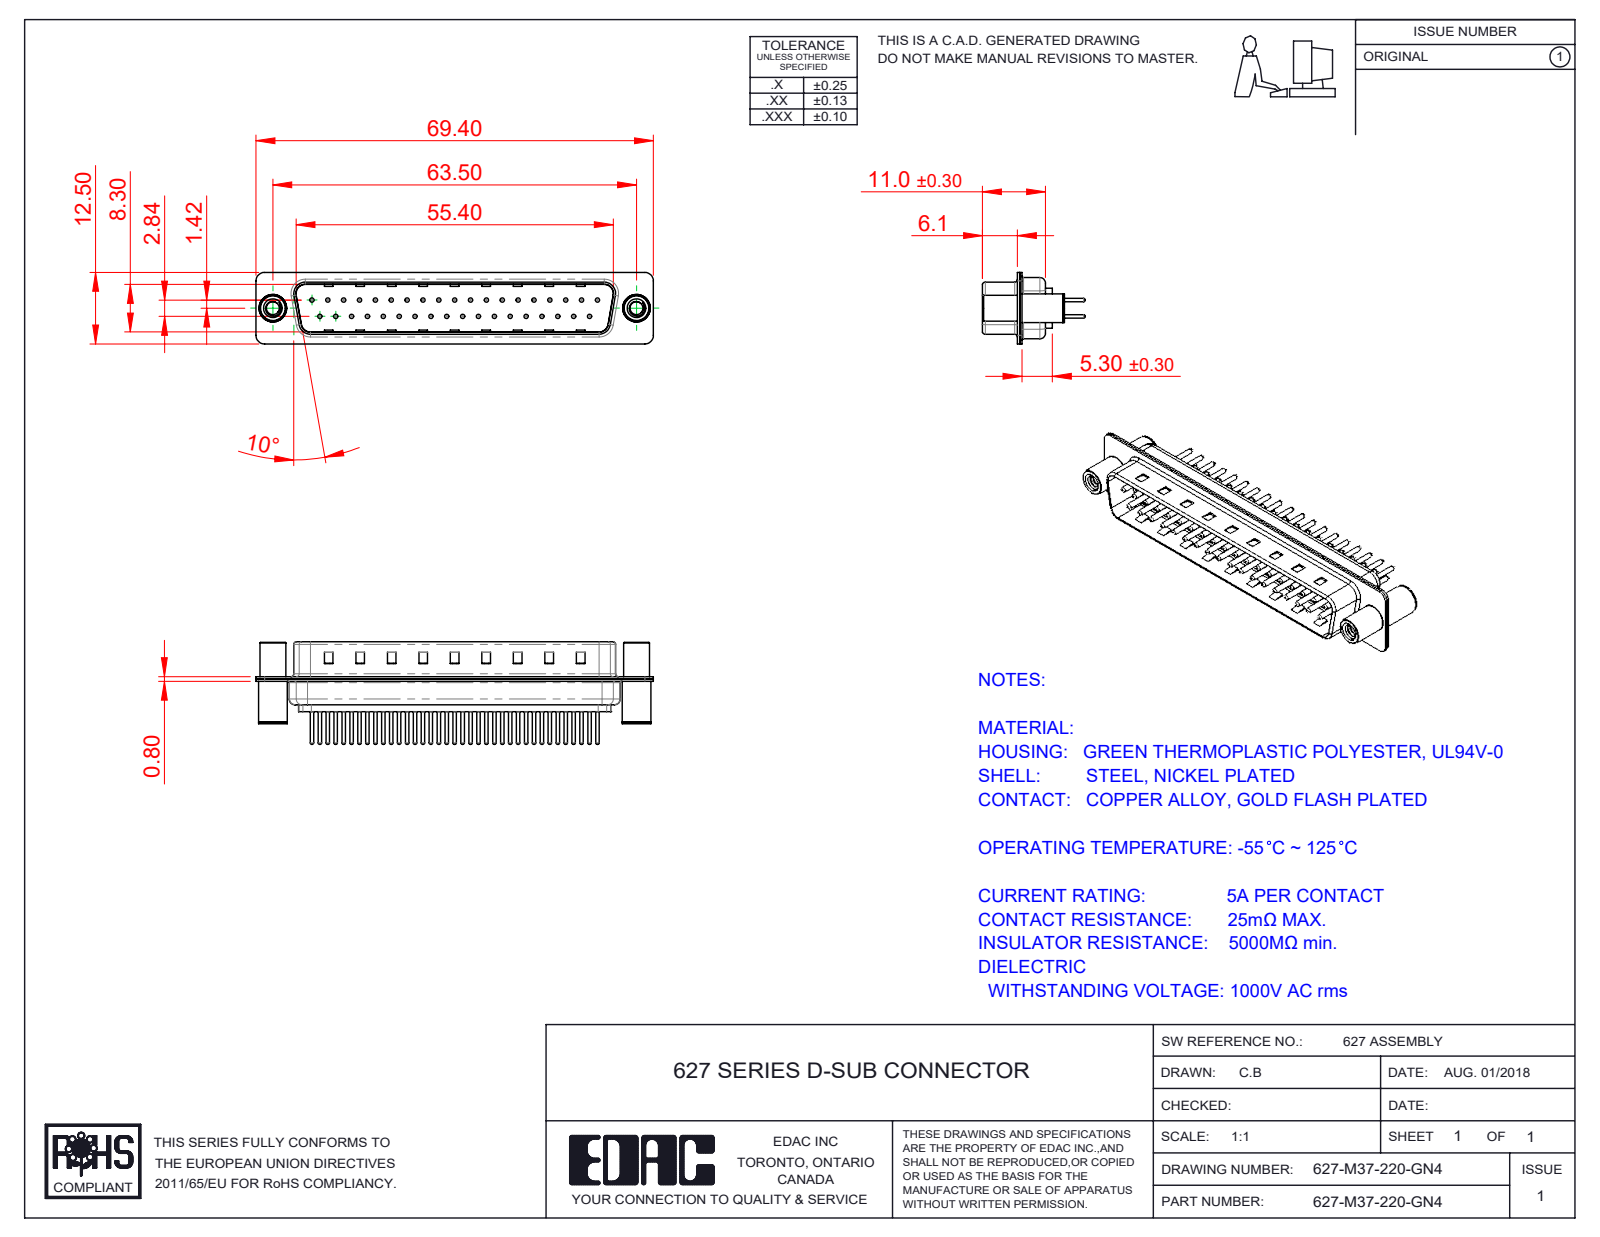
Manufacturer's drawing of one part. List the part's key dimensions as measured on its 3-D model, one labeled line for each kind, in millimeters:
Part name (STEP PRODUCT): 627-M37-220-GN4; 627M Shell Front_37 Contacts; 627M Housing_37 Contacts; 627M Shell Rear_37 Contacts (+3 more)
STEP written by: SolidWorks 2020 (CONFIG_CONTROL_DESIGN)
Units: millimetres
Bodies: 42 solids, 1867 faces (468 planar, 711 cylindrical, 688 other)
Overall size (bounding box): 69.4 × 17.9 × 12.5
Volume: 4 055 mm³ · Surface area: 9 799 mm²
Round holes (diameter × count): ⌀0.75 ×37, ⌀1.6 ×37, ⌀2 ×37, ⌀2.26 ×2, ⌀3.26 ×2, ⌀4 ×2, ⌀4.8 ×2
Round bosses / shafts (diameter × count): ⌀1.5 ×37, ⌀0.6 ×37, ⌀5 ×2, ⌀4.9 ×2, ⌀4.5 ×2
Partial cylindrical surfaces — rounded edges, fillets, slot ends (radius × count): R1.5 ×16, R2 ×12, R0.5 ×8, R1.6 ×8, R0.25 ×4, R0.6 ×4, R0.65 ×4, R0.9 ×4
Main face-to-face distances: 0.4, 0.8, 9.5, 9.1, 8.7, 9.9, 1.2, 5.7, 0.75, 0.35
Hole centre spacings: 2.77, 5.54, 3.16, 8.31, 11.08, 13.85, 16.62, 19.39
